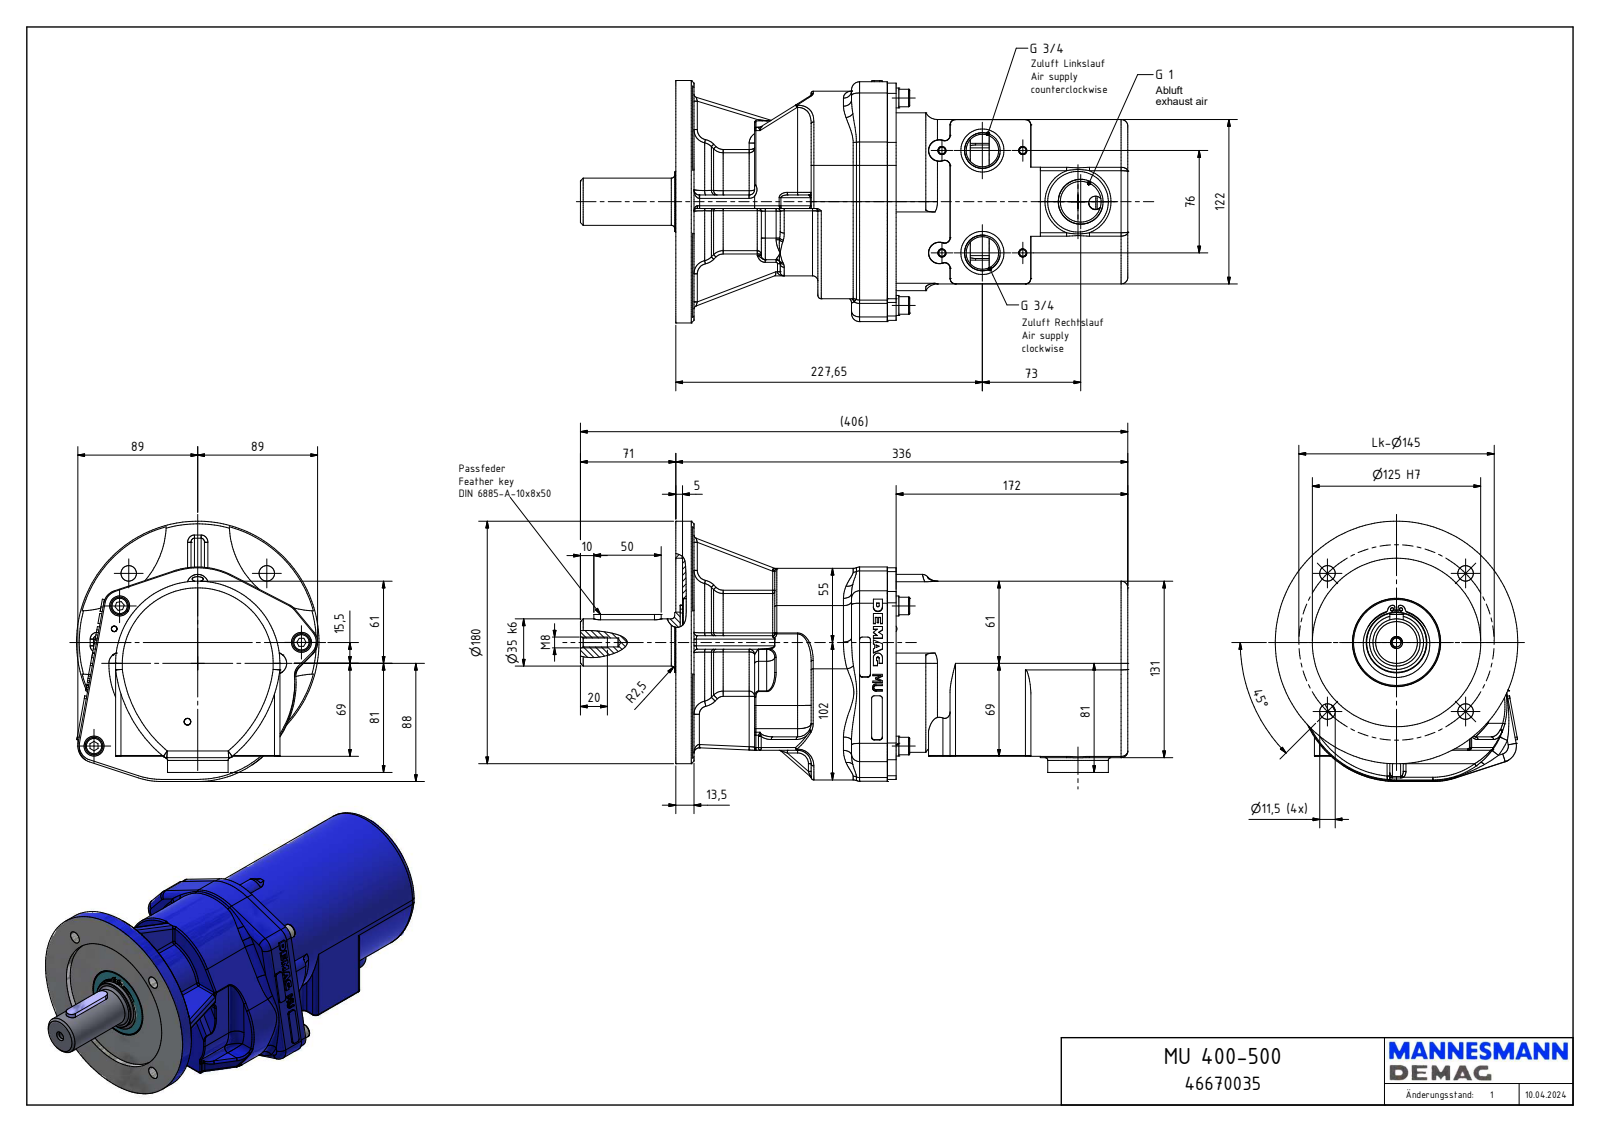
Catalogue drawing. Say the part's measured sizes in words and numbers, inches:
The part is named "MU 400-500_46670035". Its 3-D file was written by "Autodesk Inventor 2024 (AUTOMOTIVE_DESIGN)". It is 2 solids with 801 faces: 282 planar, 264 cylindrical and 255 other. Overall it measures 16.002 by 7.606 by 7.087 inches. Its volume is 284.4 cubic inches and its surface area 416.4 square inches. Round holes: 4 of diameter 0.194, 4 of diameter 0.262, 4 of diameter 0.453, 3 of diameter 0.335, 3 of diameter 0.374, 2 of diameter 0.95, 2 of diameter 1.26, 1 of diameter 0.098, 1 of diameter 0.11, 1 of diameter 0.154, 1 of diameter 0.165, 1 of diameter 0.196. Round bosses or shafts: 3 of diameter 0.583, 3 of diameter 0.512, 3 of diameter 0.315, 2 of diameter 1.772, 1 of diameter 7.087, 1 of diameter 2.559, 1 of diameter 1.673, 1 of diameter 1.378. Partial cylindrical surfaces (rounded edges, fillets, slot ends): 31 of radius 0.079, 24 of radius 0.098, 20 of radius 0.157, 12 of radius 0.236, 8 of radius 0.059, 8 of radius 0.118, 8 of radius 0.433, 6 of radius 0.039. The main face-to-face distances are 0.197, 13.215, 13.018, 0.039, 6.772, 6.246, 6.443, 12.683, 5.911, 0.335. The hole center spacings are 1.181, 3.217, 2.992, 2.258, 2.259, 2.362, 2.854, 2.855.
